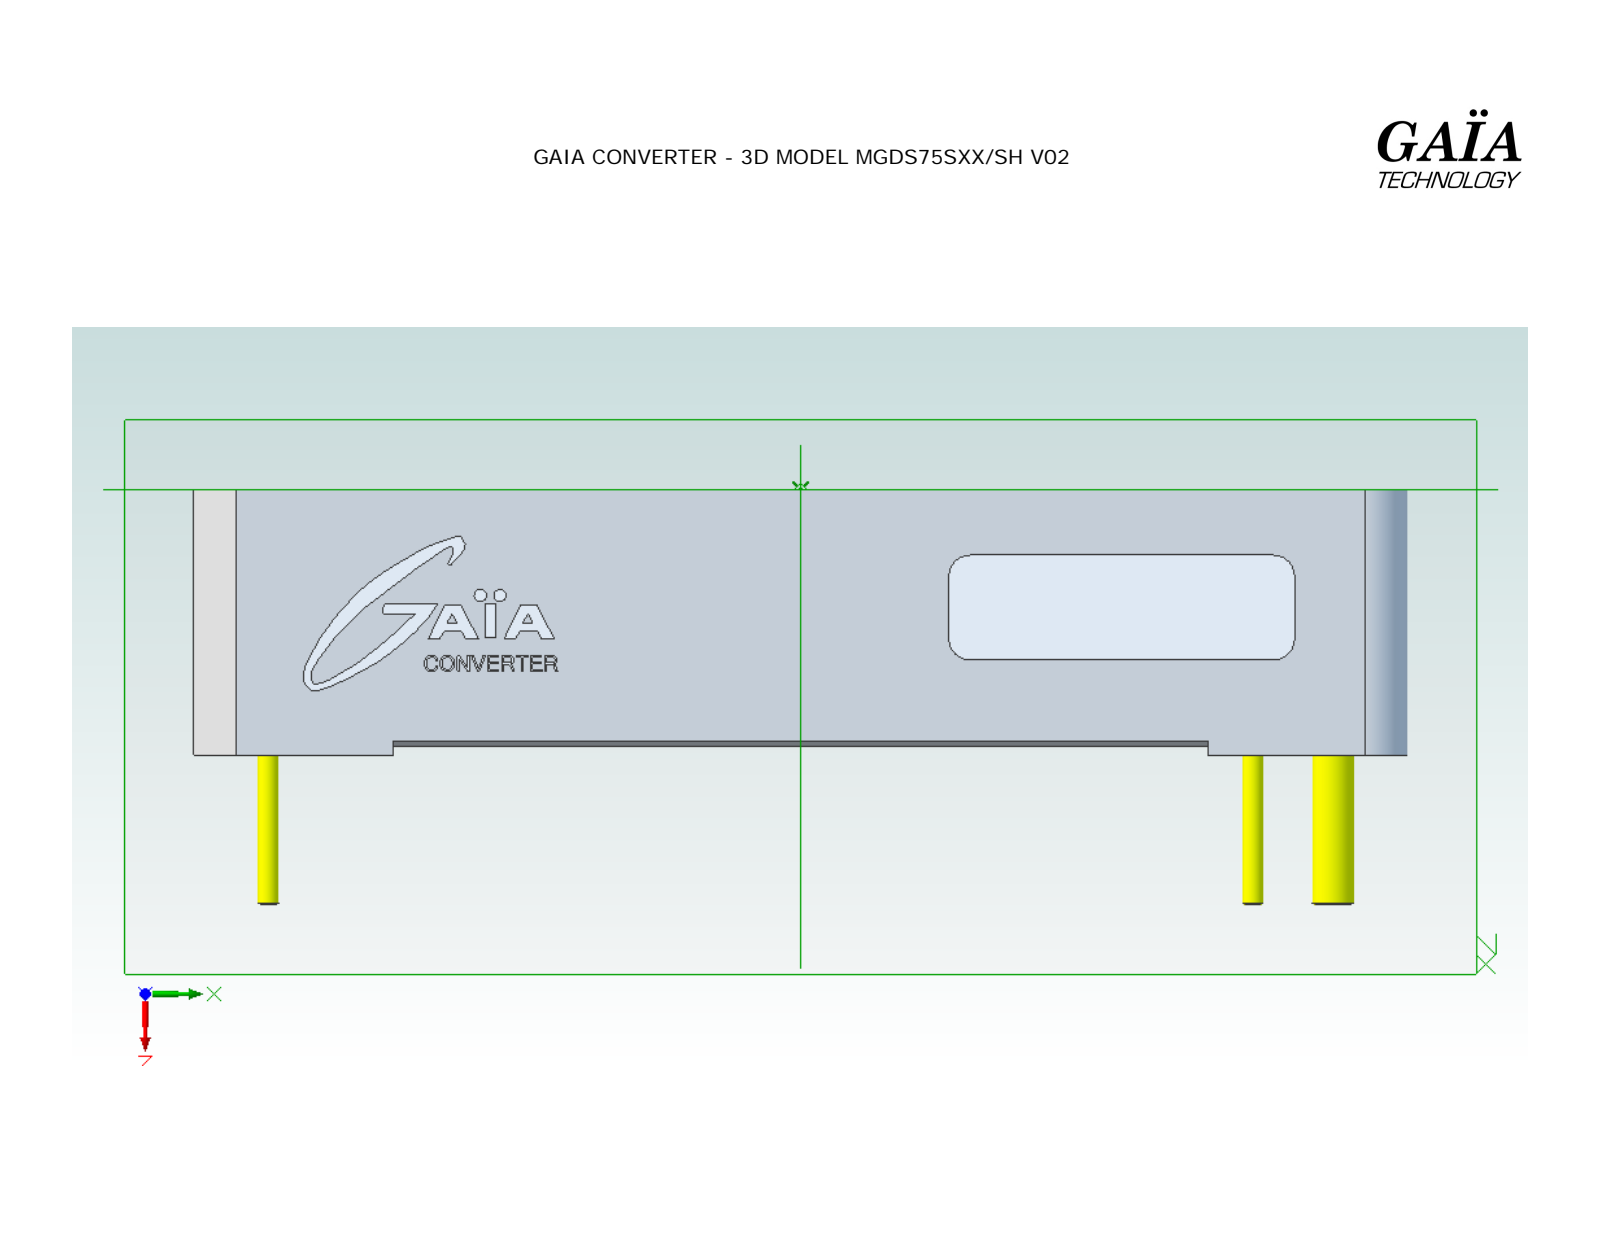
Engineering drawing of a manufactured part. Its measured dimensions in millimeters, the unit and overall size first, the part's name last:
Units: millimetres
Overall size (bounding box): 57.9 × 36.81 × 19.85
Round holes (diameter × count): ⌀3.3 ×4, ⌀1 ×1
Round bosses / shafts (diameter × count): ⌀2.3 ×8, ⌀1 ×8, ⌀2.5 ×2, ⌀2 ×2, ⌀0.59 ×1, ⌀0.58 ×1
Partial cylindrical surfaces — rounded edges, fillets, slot ends (radius × count): R2.65 ×14, R0.49 ×9, R2 ×8, R2.35 ×8, R1 ×4, R2.3 ×4, R2 ×1
Main face-to-face distances: 12, 5.35, 6.65, 11.8, 6.45, 12.3, 6.95, 0.5, 11.81, 6.46
Hole centre spacings: 31.94, 52, 61.03, 12.17, 19.79, 52.82, 55.07
Volume: 13 248 mm³ · Surface area: 16 276 mm²
Bodies: 1 solid, 490 faces (335 planar, 101 cylindrical, 54 other)
Part name (STEP PRODUCT): MGDS75SXX_SH_V02_BOOLEAN_FOR_STEP
STEP written by: Alibre (AUTOMOTIVE_DESIGN)
